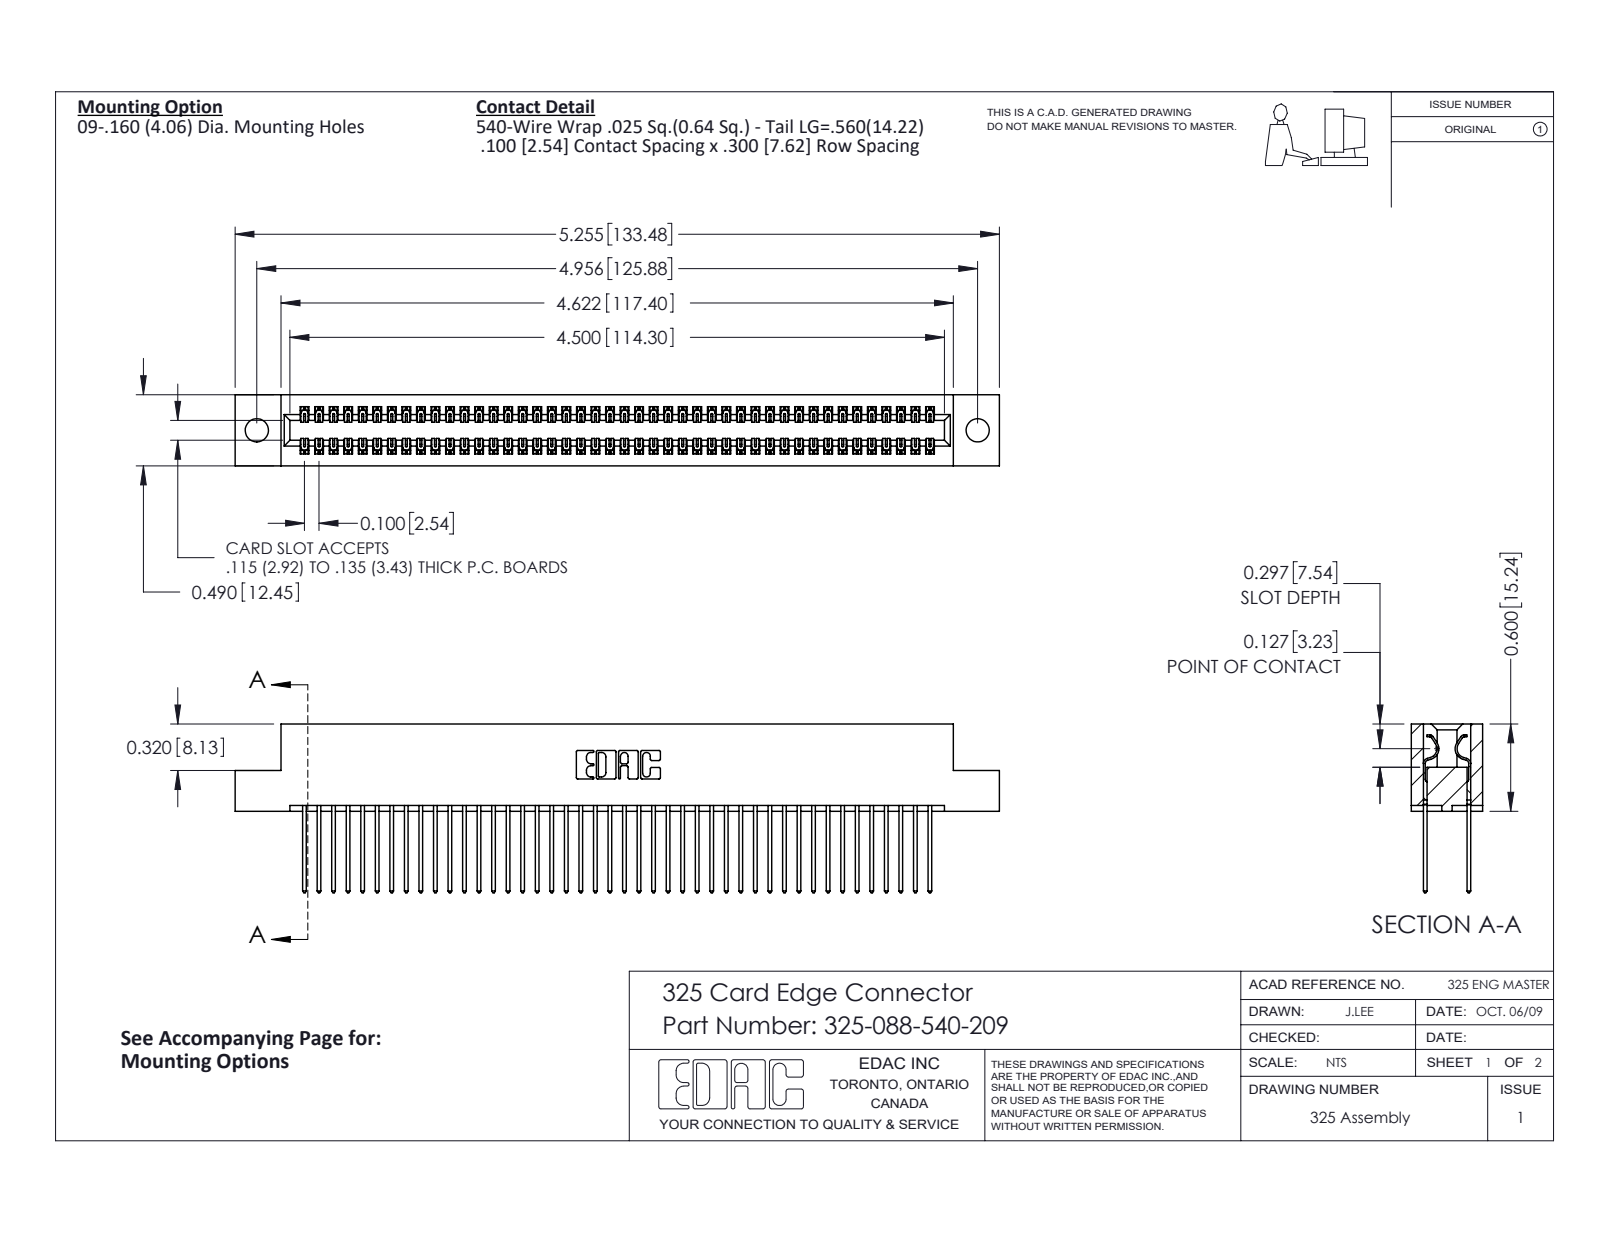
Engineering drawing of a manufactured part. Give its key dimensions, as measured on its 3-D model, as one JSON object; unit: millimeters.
{"part_name": "325-292-001_325-293-140; 325-088-540-209; 325 Part_.160 TH", "step_written_by": "SolidWorks 2016 (CONFIG_CONTROL_DESIGN)", "units": "millimeters", "bodies": {"solids": 89, "faces": 4690, "planar": 3238, "cylindrical": 1452, "other": 0}, "overall_size": [133.5, 29.5, 12.4], "volume_mm3": 17350, "surface_area_mm2": 22560, "round_holes": [[4.1, 2]], "partial_cylinders_radius": [[0.2, 132], [0.3, 88], [0.3, 22], [0.2, 6], [0.8, 6], [0.7, 3], [0.4, 2], [0.6, 2]], "face_to_face_distances": [2.1, 10.3, 7.6, 2.7, 9.7, 0.6, 8.3, 12.4, 7, 14.2], "hole_center_spacings": [125.9]}
